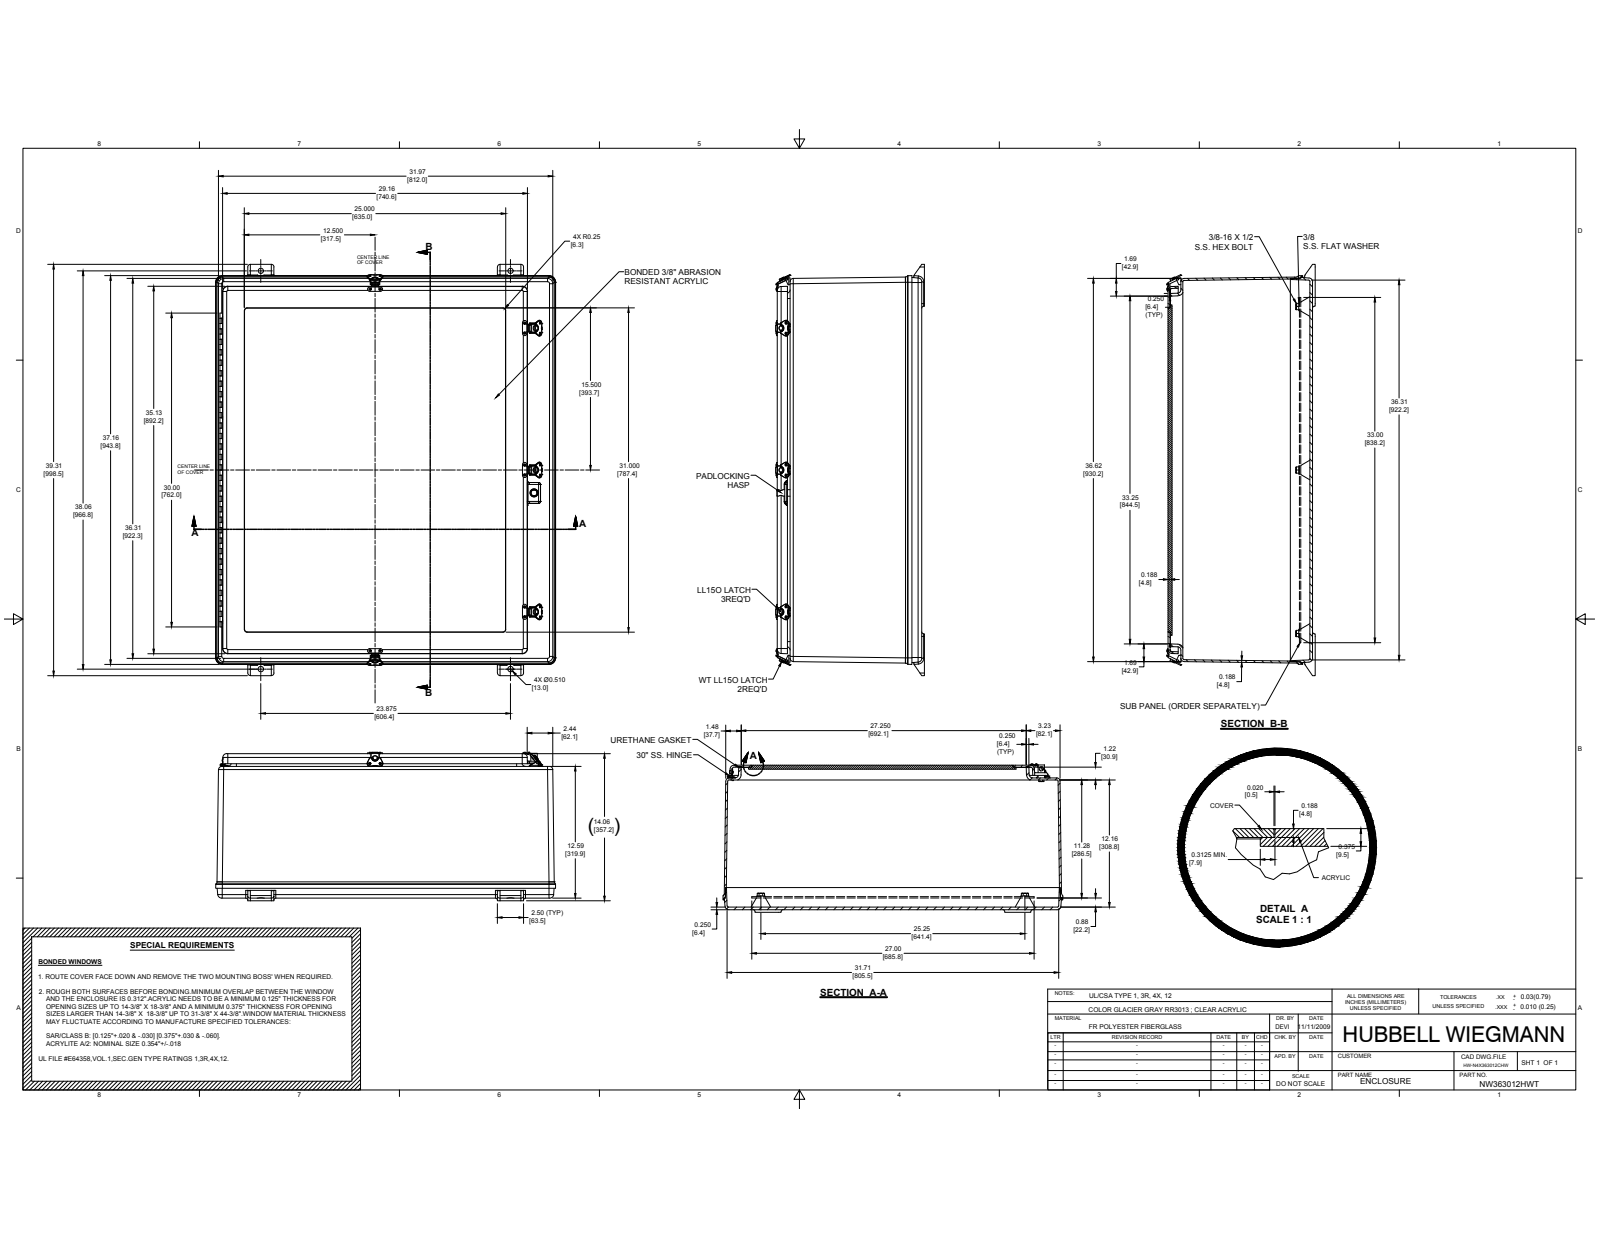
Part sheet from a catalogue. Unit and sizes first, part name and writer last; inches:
Units: inches
Overall size (bounding box): 39.313 × 32.5 × 14.213
Round holes (diameter × count): ⌀0.13 ×36, ⌀0.063 ×20, ⌀0.138 ×10, ⌀0.187 ×10, ⌀0.065 ×8, ⌀0.307 ×6, ⌀0.563 ×4, ⌀0.135 ×3, ⌀0.156 ×3, ⌀0.433 ×2, ⌀0.5 ×2, ⌀0.51 ×2
Round bosses / shafts (diameter × count): ⌀0.14 ×20, ⌀0.297 ×8, ⌀0.5 ×5, ⌀0.2 ×3, ⌀0.563 ×2, ⌀0.25 ×1, ⌀0.201 ×1
Partial cylindrical surfaces — rounded edges, fillets, slot ends (radius × count): R0.01 ×127, R0.25 ×28, R0.313 ×23, R0.187 ×21, R0.03 ×20, R0.375 ×13, R0.5 ×12, R0.063 ×10
Main face-to-face distances: 0.25, 0.188, 13.817, 13.567, 13.442, 13.192, 0.375, 0.187, 1.223, 0.187
Hole centre spacings: 13.563, 9.5, 19.5, 1, 3.474, 13.583, 15.625, 19.044
Volume: 1 078 in³ · Surface area: 9 500 in²
Bodies: 70 solids, 1939 faces (747 planar, 760 cylindrical, 432 other)
Part name (STEP PRODUCT): WPN3630B; WPN363012SHWT; SS HINGE COVER (30); 0.13 RIVET PIN (+7 more)
STEP written by: Autodesk Inventor 2014 (AUTOMOTIVE_DESIGN)
